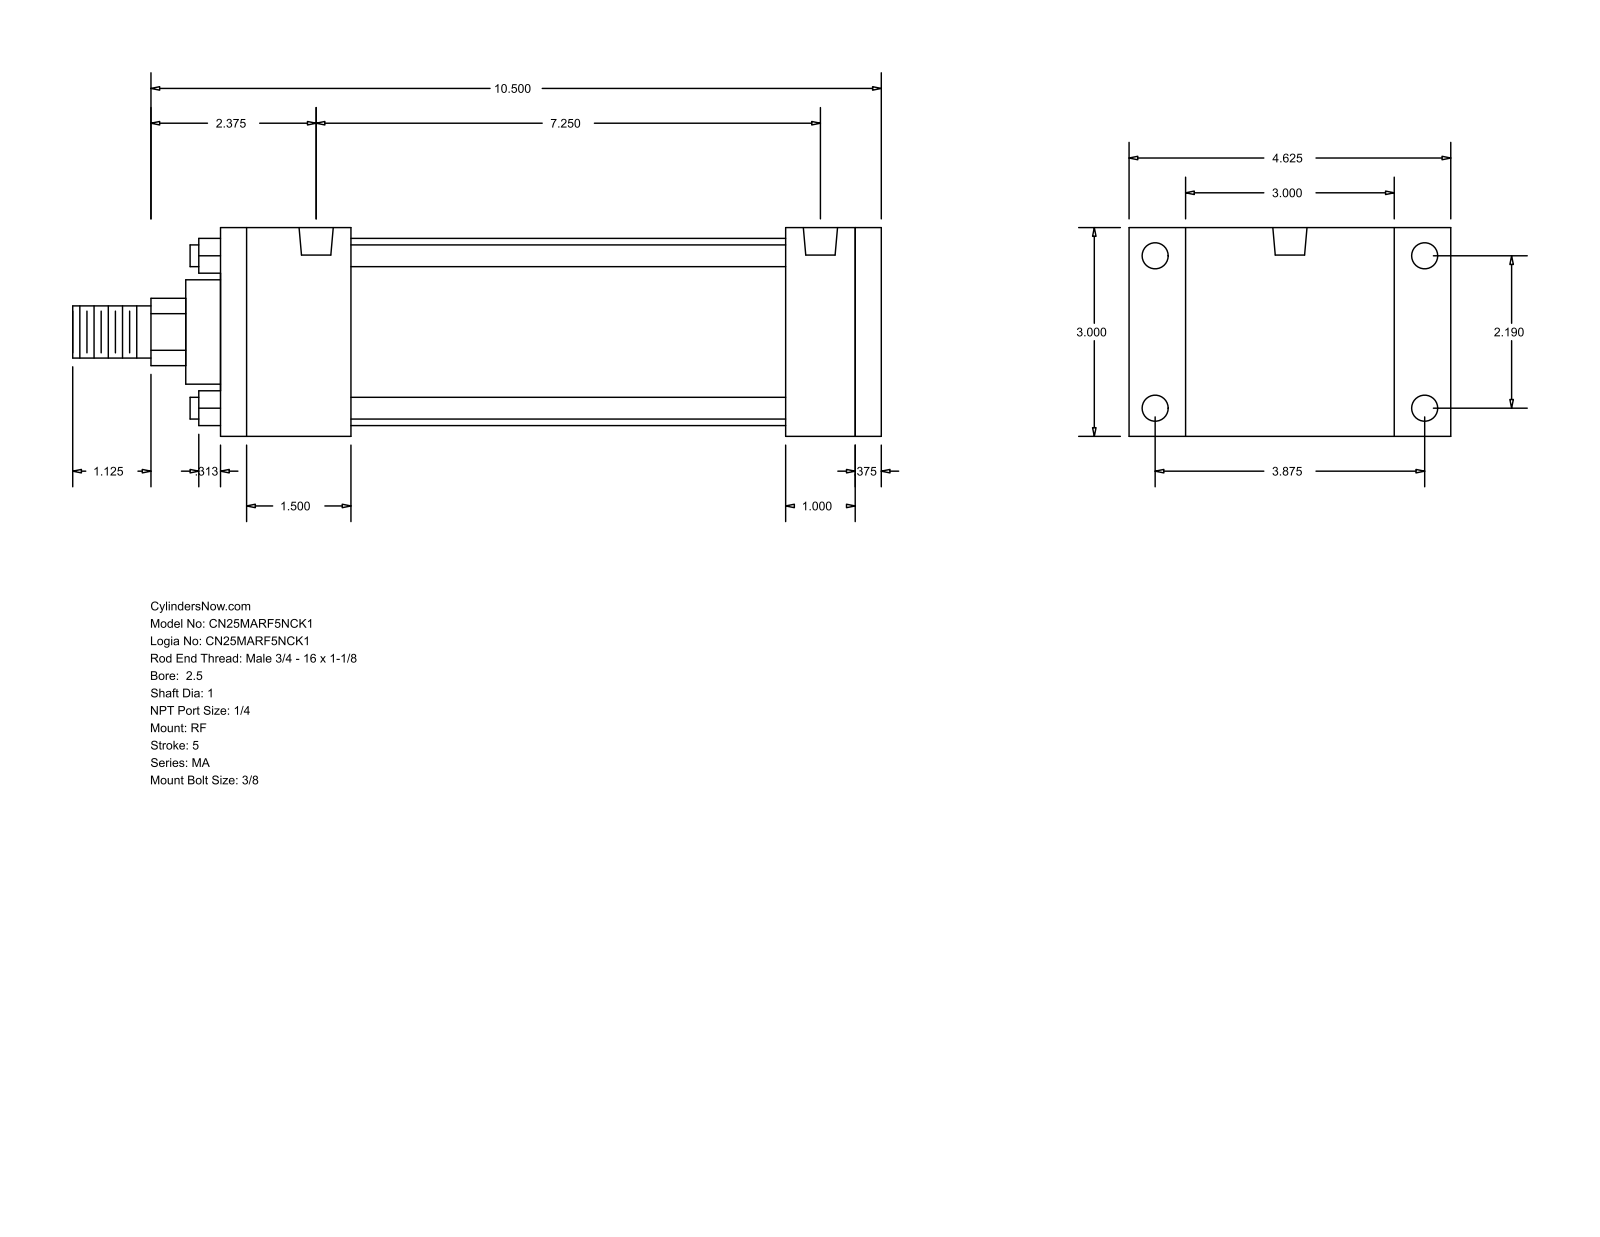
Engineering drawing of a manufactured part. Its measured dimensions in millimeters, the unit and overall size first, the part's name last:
Units: millimetres
Overall size (bounding box): 295.27 × 117.47 × 76.2
Round holes (diameter × count): ⌀7.94 ×4, ⌀9.53 ×4, ⌀12.49 ×2
Round bosses / shafts (diameter × count): ⌀7.94 ×4, ⌀68.33 ×1, ⌀38.1 ×1, ⌀25.4 ×1, ⌀19.05 ×1
Partial cylindrical surfaces — rounded edges, fillets, slot ends (radius × count): R12.29 ×1
Main face-to-face distances: 76.2, 241.3, 231.78, 9.52, 25.4, 47.63, 206.38, 158.75, 184.15, 193.67
Hole centre spacings: 55.62, 98.42, 113.05, 184.14
Bodies: 0 solids, 92 faces (64 planar, 28 cylindrical, 0 other)
Part name (STEP PRODUCT): MA_RF__0250_1
STEP written by: GSSL Pune (CONFIG_CONTROL_DESIGN)
